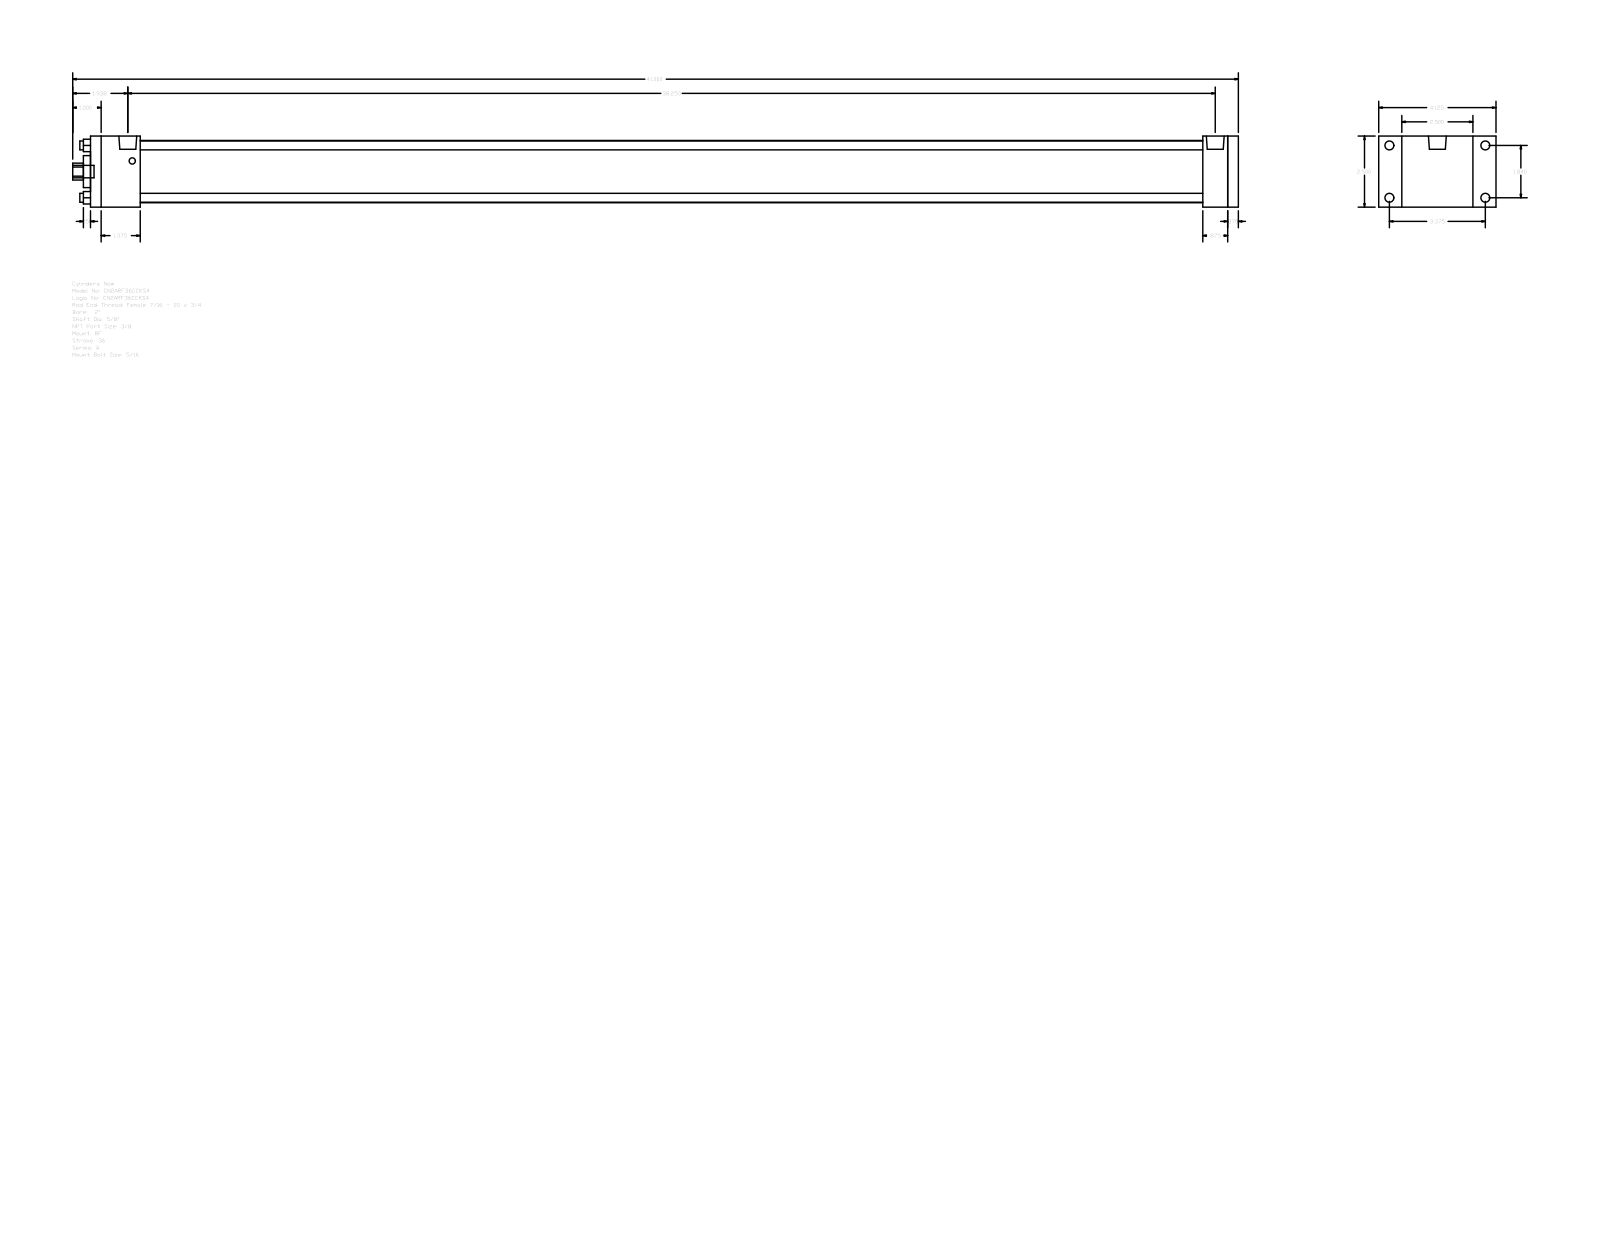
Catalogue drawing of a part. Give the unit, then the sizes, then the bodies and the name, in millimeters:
Units: millimetres
Overall size (bounding box): 1041.4 × 104.78 × 63.5
Round holes (diameter × count): ⌀7.94 ×4, ⌀15.88 ×1, ⌀28.57 ×1, ⌀55.63 ×1
Round bosses / shafts (diameter × count): ⌀7.94 ×4, ⌀5.56 ×4, ⌀15.93 ×2, ⌀11.11 ×1
Partial cylindrical surfaces — rounded edges, fillets, slot ends (radius × count): R7.54 ×1
Main face-to-face distances: 63.5, 1025.52, 9.52, 1016, 44.45, 971.55, 981.07, 993.77, 949.32, 22.23
Hole centre spacings: 33.05, 46.74, 66.1
Bodies: 0 solids, 92 faces (64 planar, 28 cylindrical, 0 other)
Part name (STEP PRODUCT): A_RF__0200_0.625
STEP written by: GSSL Pune (CONFIG_CONTROL_DESIGN)
